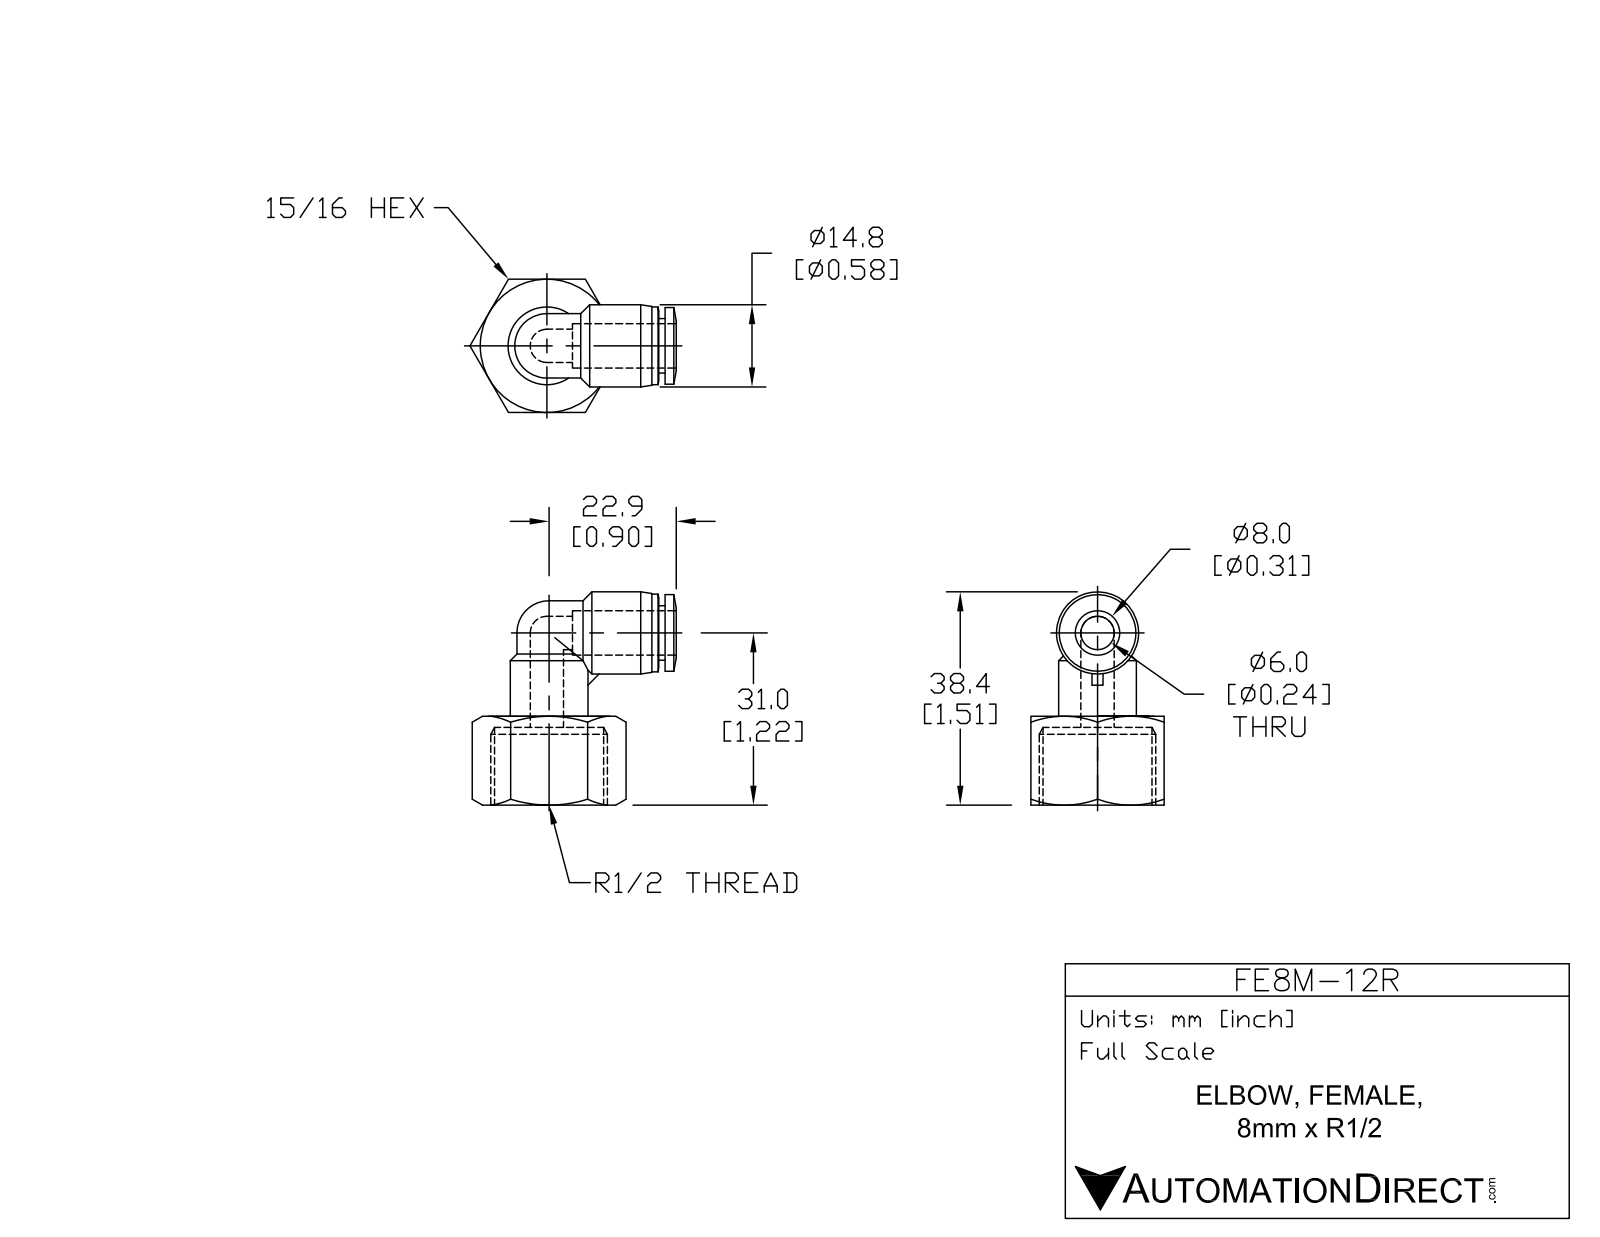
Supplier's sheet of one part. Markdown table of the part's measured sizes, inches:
| quantity | value |
| --- | --- |
| part name | FE8M-12R |
| STEP written by | SolidWorks 2015 (AUTOMOTIVE_DESIGN) |
| units | inches |
| bodies | 1 solid, 67 faces (17 planar, 19 cylindrical, 31 other) |
| overall size | 1.512 × 1.447 × 0.945 |
| volume | 0.429 in³ |
| surface area | 8.829 in² |
| round holes (diameter × count) | 0.236 × 2, 0.327 × 1 |
| round bosses / shafts (diameter × count) | 0.551 × 2, 0.583 × 1, 0.543 × 1, 0.457 × 1, 0.386 × 1 |
| partial cylindrical surfaces (radius × count) | 0.228 × 1 |
| main face-to-face distances | 0.945, 0.079, 0.551, 0.63, 0.045, 0.596, 0.642, 0.72, 0.124, 0.433 |
